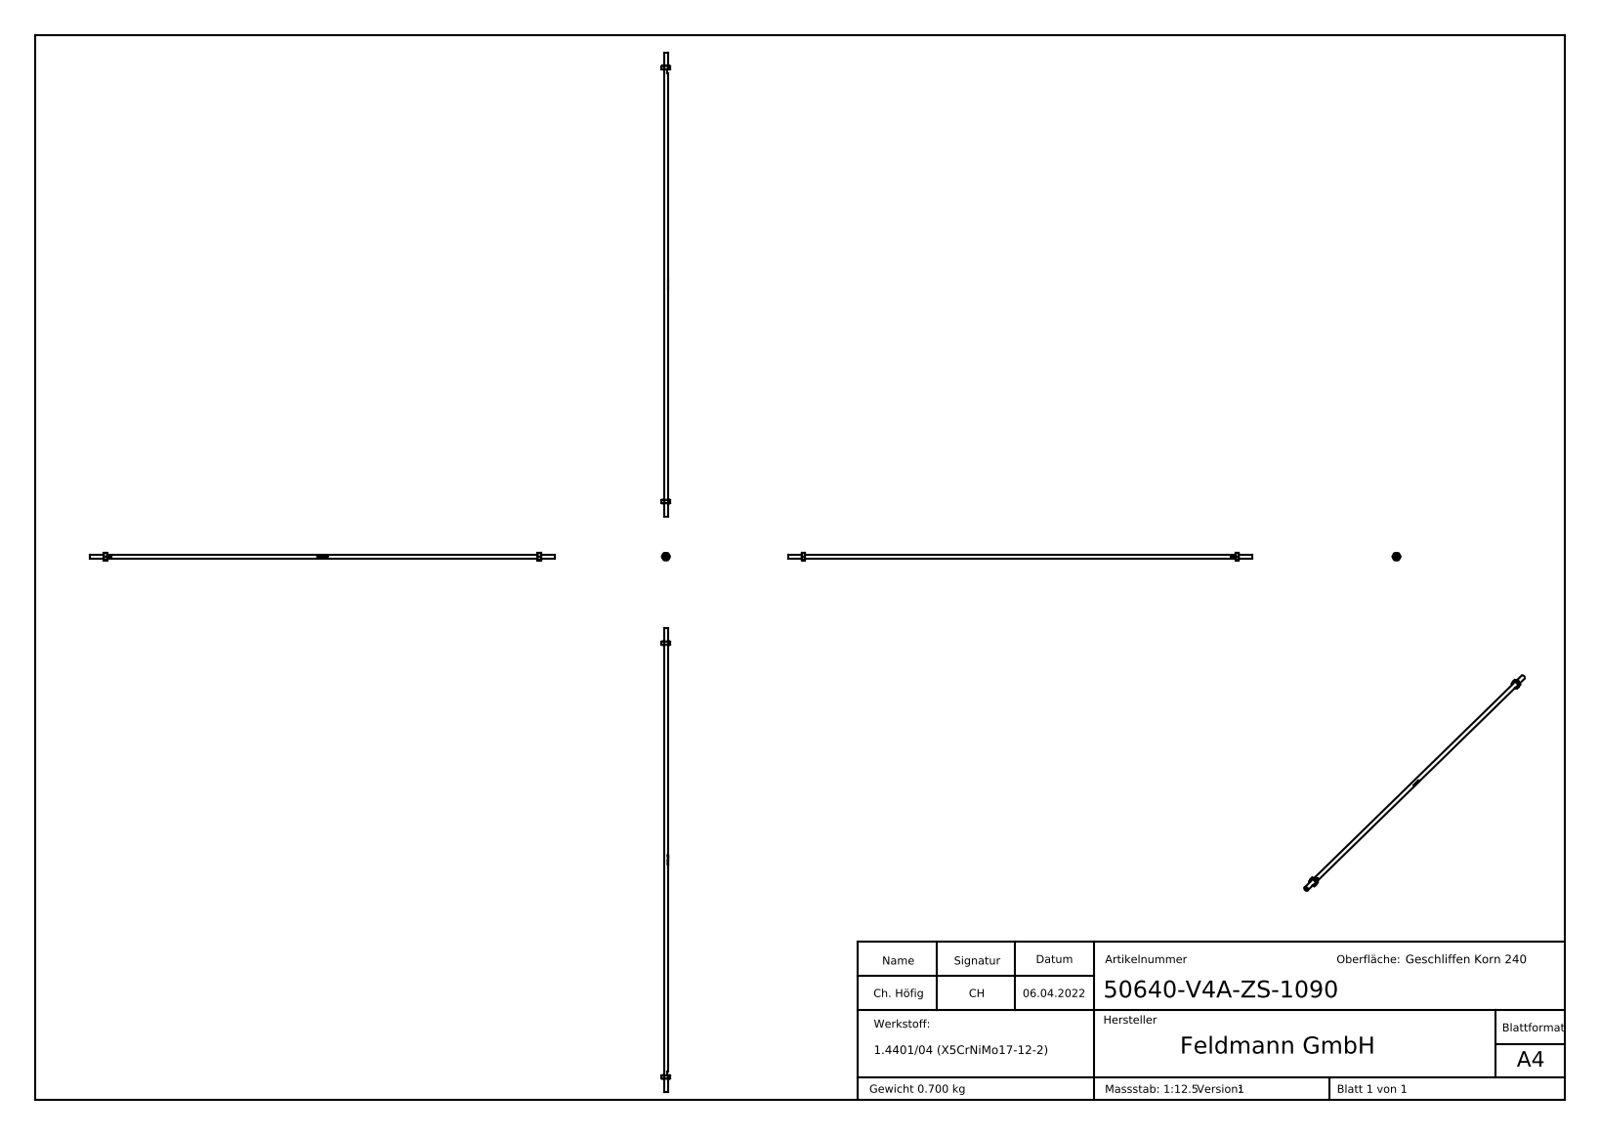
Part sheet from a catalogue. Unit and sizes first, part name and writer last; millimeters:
Units: millimetres
Overall size (bounding box): 1090 × 19.48 × 17
Round holes (diameter × count): ⌀8.5 ×1
Round bosses / shafts (diameter × count): ⌀10 ×1
Partial cylindrical surfaces — rounded edges, fillets, slot ends (radius × count): R0.5 ×6
Main face-to-face distances: 17, 8, 1018, 1010, 1026, 32, 40, 1050, 1058, 1090
Volume: 88 583 mm³ · Surface area: 36 539 mm²
Bodies: 3 solids, 1247 faces (648 planar, 34 cylindrical, 565 other)
Part name (STEP PRODUCT): 50640-V4A-ZS-1090; 50640-XXX-ZS_50640-V4A-ZS-1090; DIN 934 M4-M20_58321-240-10
STEP written by: SolidWorks 2018 (CONFIG_CONTROL_DESIGN)
